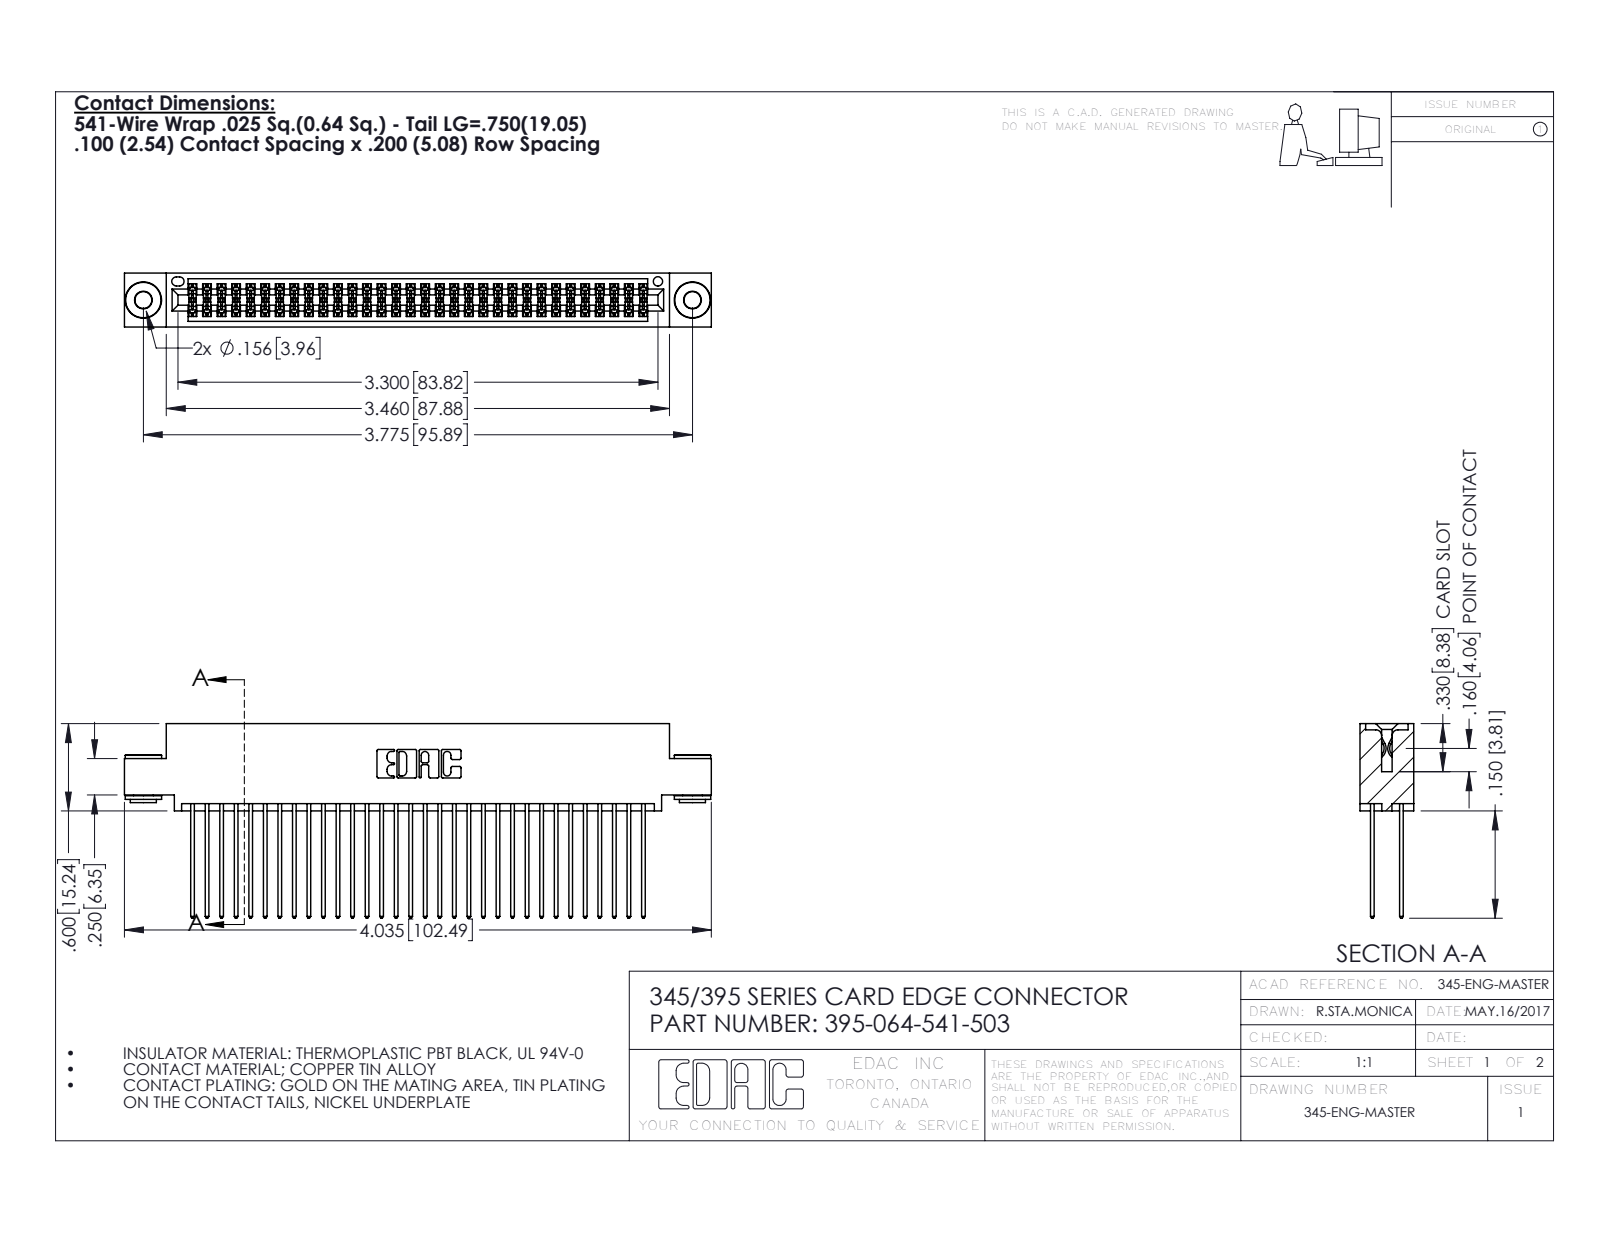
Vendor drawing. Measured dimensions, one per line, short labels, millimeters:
name: 345-250-002_345-250-002-102; 395-064-541-503; 345 Part_0.110 Offset - 0.156 Dia-TH; 345-292-001_345-293-141
written by: SolidWorks 2016 (CONFIG_CONTROL_DESIGN)
unit: mm
bodies: 67 solids, 3368 faces (2206 planar, 1154 cylindrical, 8 other)
size: 102.5 × 34 × 9.4
volume: 10 200 mm³; area: 16 870 mm²
holes: 2× ⌀2.9, 2× ⌀4, 1× ⌀1.6
bosses: 2× ⌀6.4, 2× ⌀4.6, 2× ⌀3.5
rounds: 96× R0.2, 64× R0.3, 22× R0.3, 6× R0.2, 6× R0.8, 3× R0.7, 2× R0.4, 2× R0.5
face distances: 1.8, 7.6, 5.1, 0.6, 2.5, 6.9, 5.7, 9.4, 4.4, 3.8
hole spacings: 6.9, 89.9, 95.9
